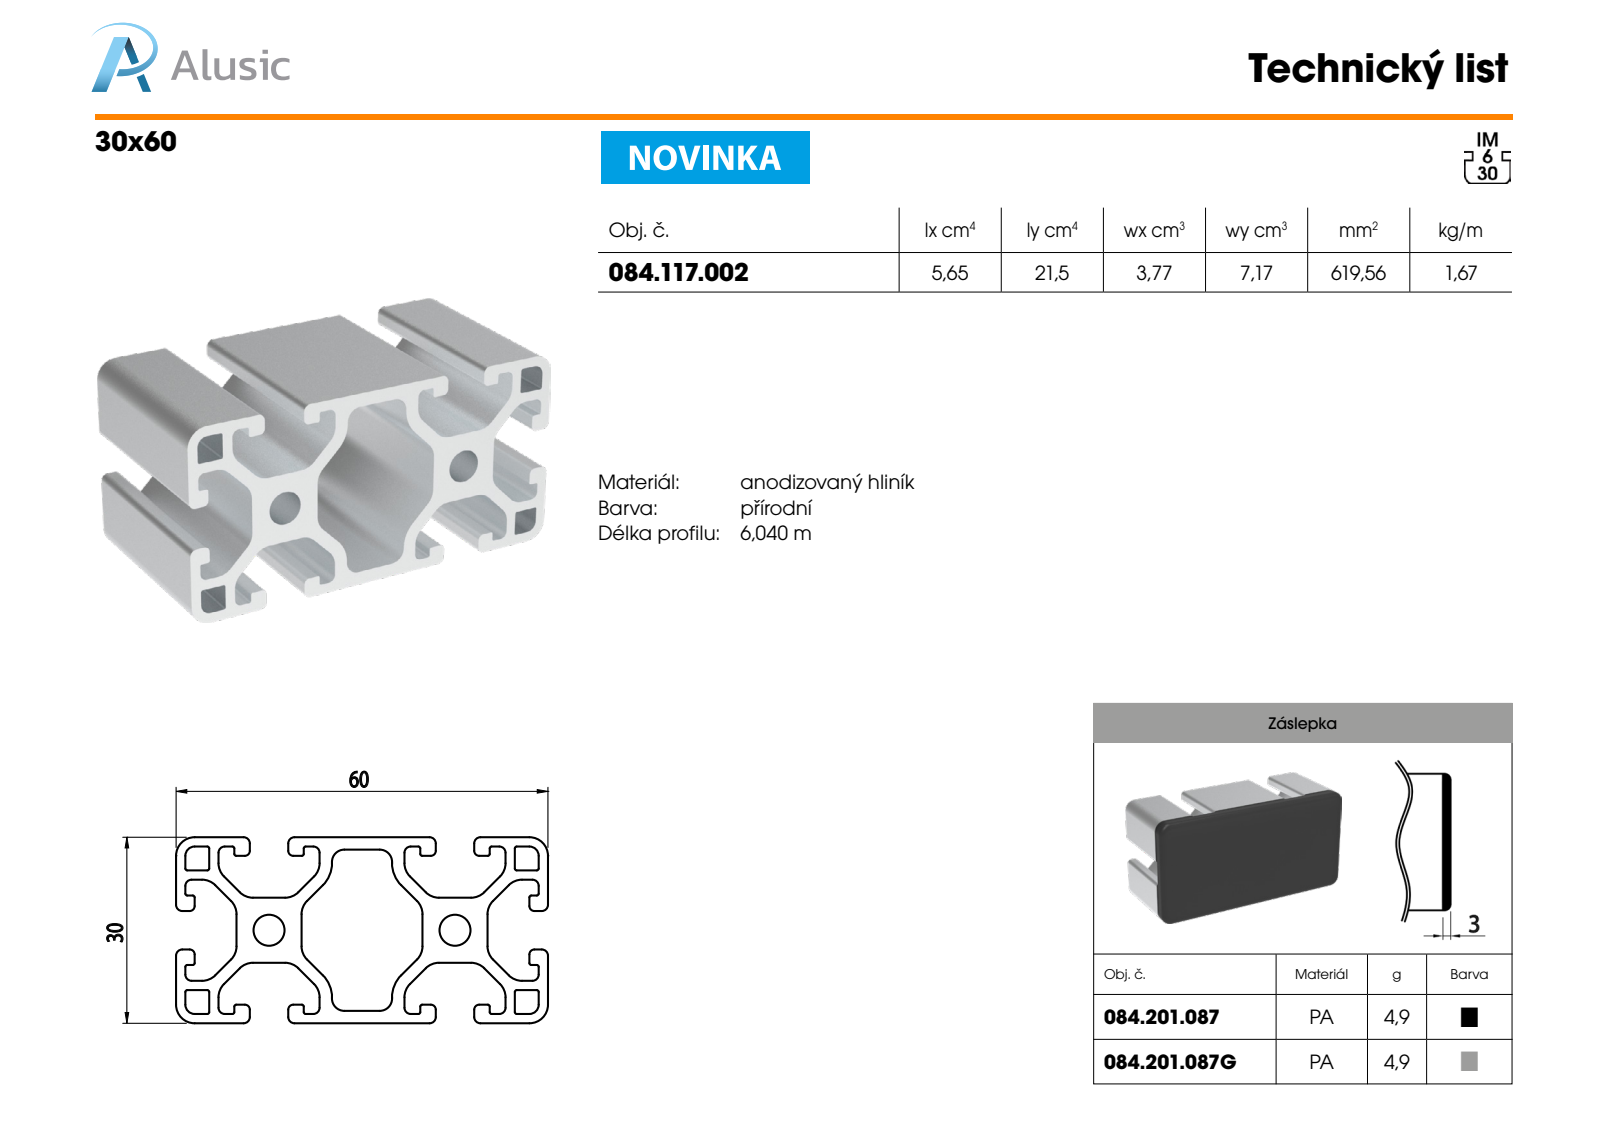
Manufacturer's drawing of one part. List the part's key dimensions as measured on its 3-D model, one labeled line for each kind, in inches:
Part name (STEP PRODUCT): 084.117.002
STEP written by: SolidWorks 2018 (AUTOMOTIVE_DESIGN)
Units: inches
Bodies: 1 solid, 238 faces (118 planar, 120 cylindrical, 0 other)
Overall size (bounding box): 3.937 × 2.362 × 1.181
Volume: 3.781 in³ · Surface area: 88.99 in²
Round holes (diameter × count): ⌀0.197 ×2
Partial cylindrical surfaces — rounded edges, fillets, slot ends (radius × count): R0.012 ×36, R0.118 ×32, R0.039 ×24, R0.031 ×12, R0.059 ×4, R0.079 ×4, R0.197 ×4
Main face-to-face distances: 0.059, 1.181, 0.079, 0.211, 0.152, 0.738, 0.797, 0.384, 0.852, 0.835
Hole centre spacings: 1.181
